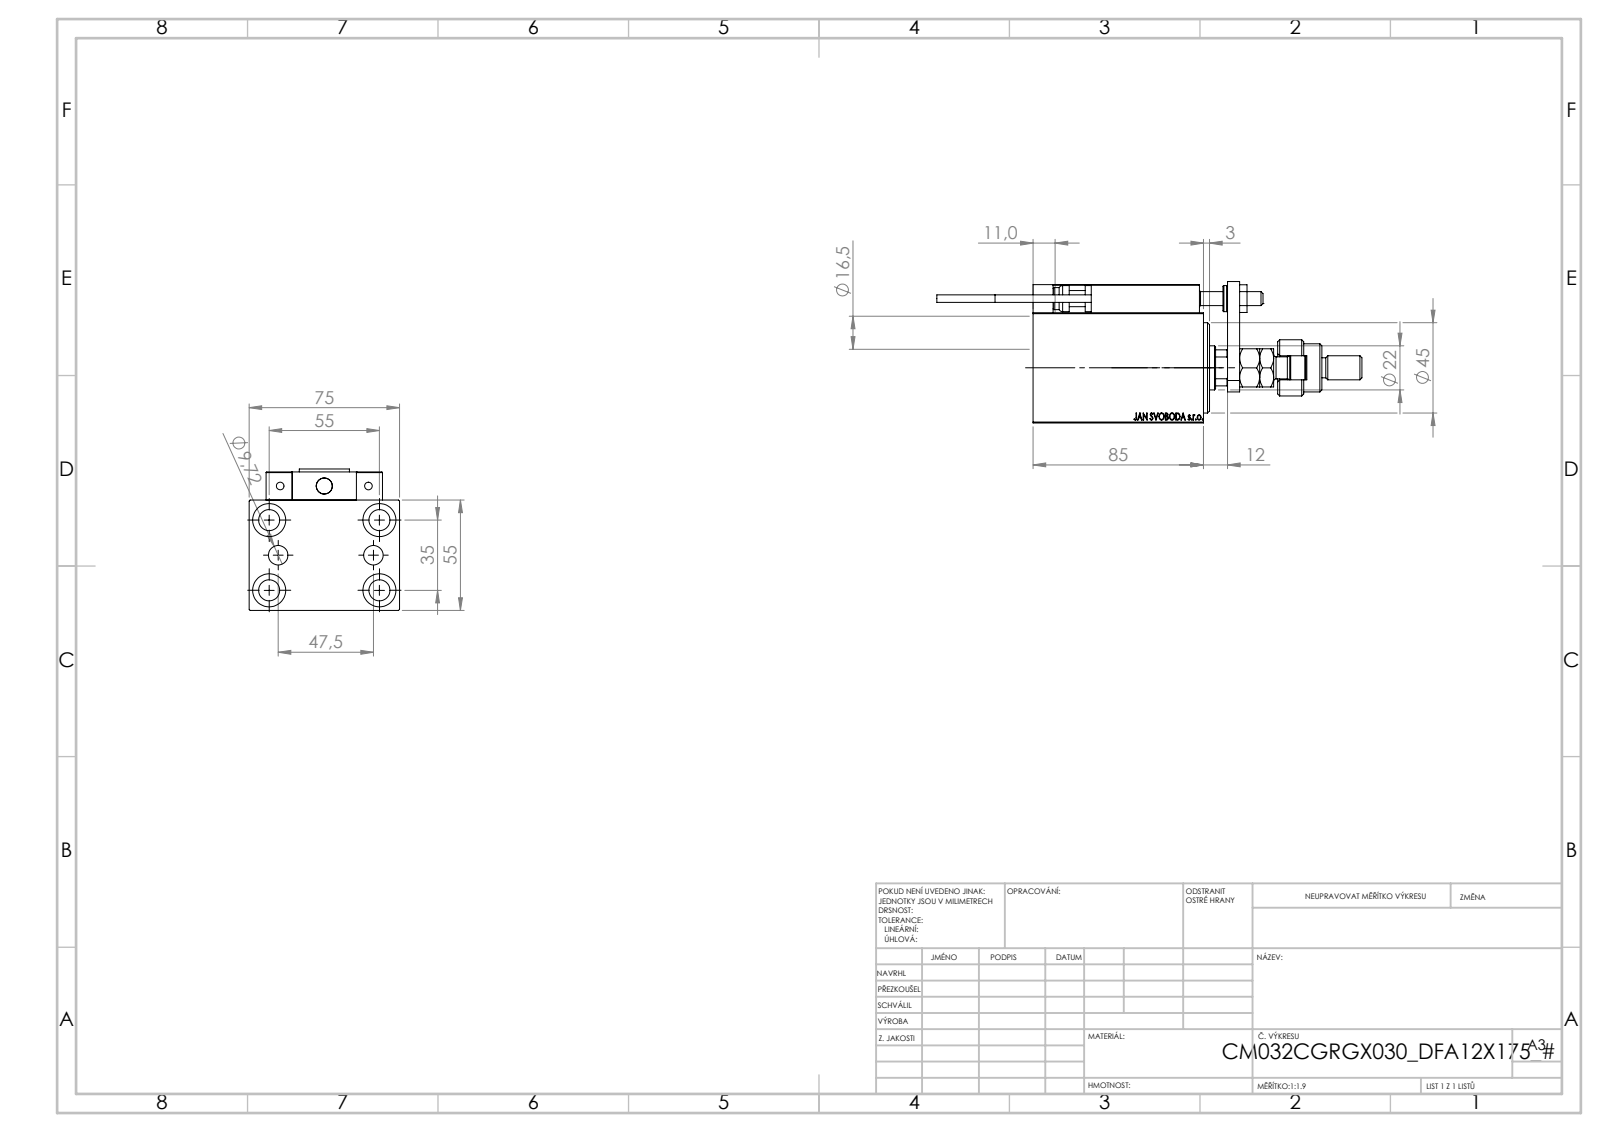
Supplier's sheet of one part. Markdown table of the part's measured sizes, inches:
| quantity | value |
| --- | --- |
| part name | MFA; V450CM_VC_B; TYC_L79; ZARAZKA (+7 more) |
| STEP written by | SolidWorks 2019 (CONFIG_CONTROL_DESIGN) |
| units | inches |
| bodies | 25 solids, 1363 faces (588 planar, 197 cylindrical, 578 other) |
| overall size | 8.346 × 2.953 × 2.776 |
| volume | 22.31 in³ |
| surface area | 146.5 in² |
| round holes (diameter × count) | 0.157 × 6, 0.315 × 5, 0.413 × 5, 0.65 × 5, 0.126 × 4, 0.197 × 2, 0.383 × 2, 0.276 × 1, 0.866 × 1, 1.004 × 1, 1.26 × 1, 1.339 × 1 |
| round bosses / shafts (diameter × count) | 0.433 × 2, 0.197 × 2, 0.15 × 2, 1.102 × 1, 0.945 × 1, 0.709 × 1, 0.512 × 1, 0.472 × 1 |
| partial cylindrical surfaces (radius × count) | 0.012 × 30, 0.118 × 2, 0.384 × 1, 0.413 × 1 |
| main face-to-face distances | 2.165, 2.953, 0.551, 2.717, 0.709, 0.197, 0.984, 0.236, 0.472, 0.394 |
| hole center spacings | 0.705, 1.283, 2.132, 0.448, 0.787, 0.935, 1.165, 1.169 |
